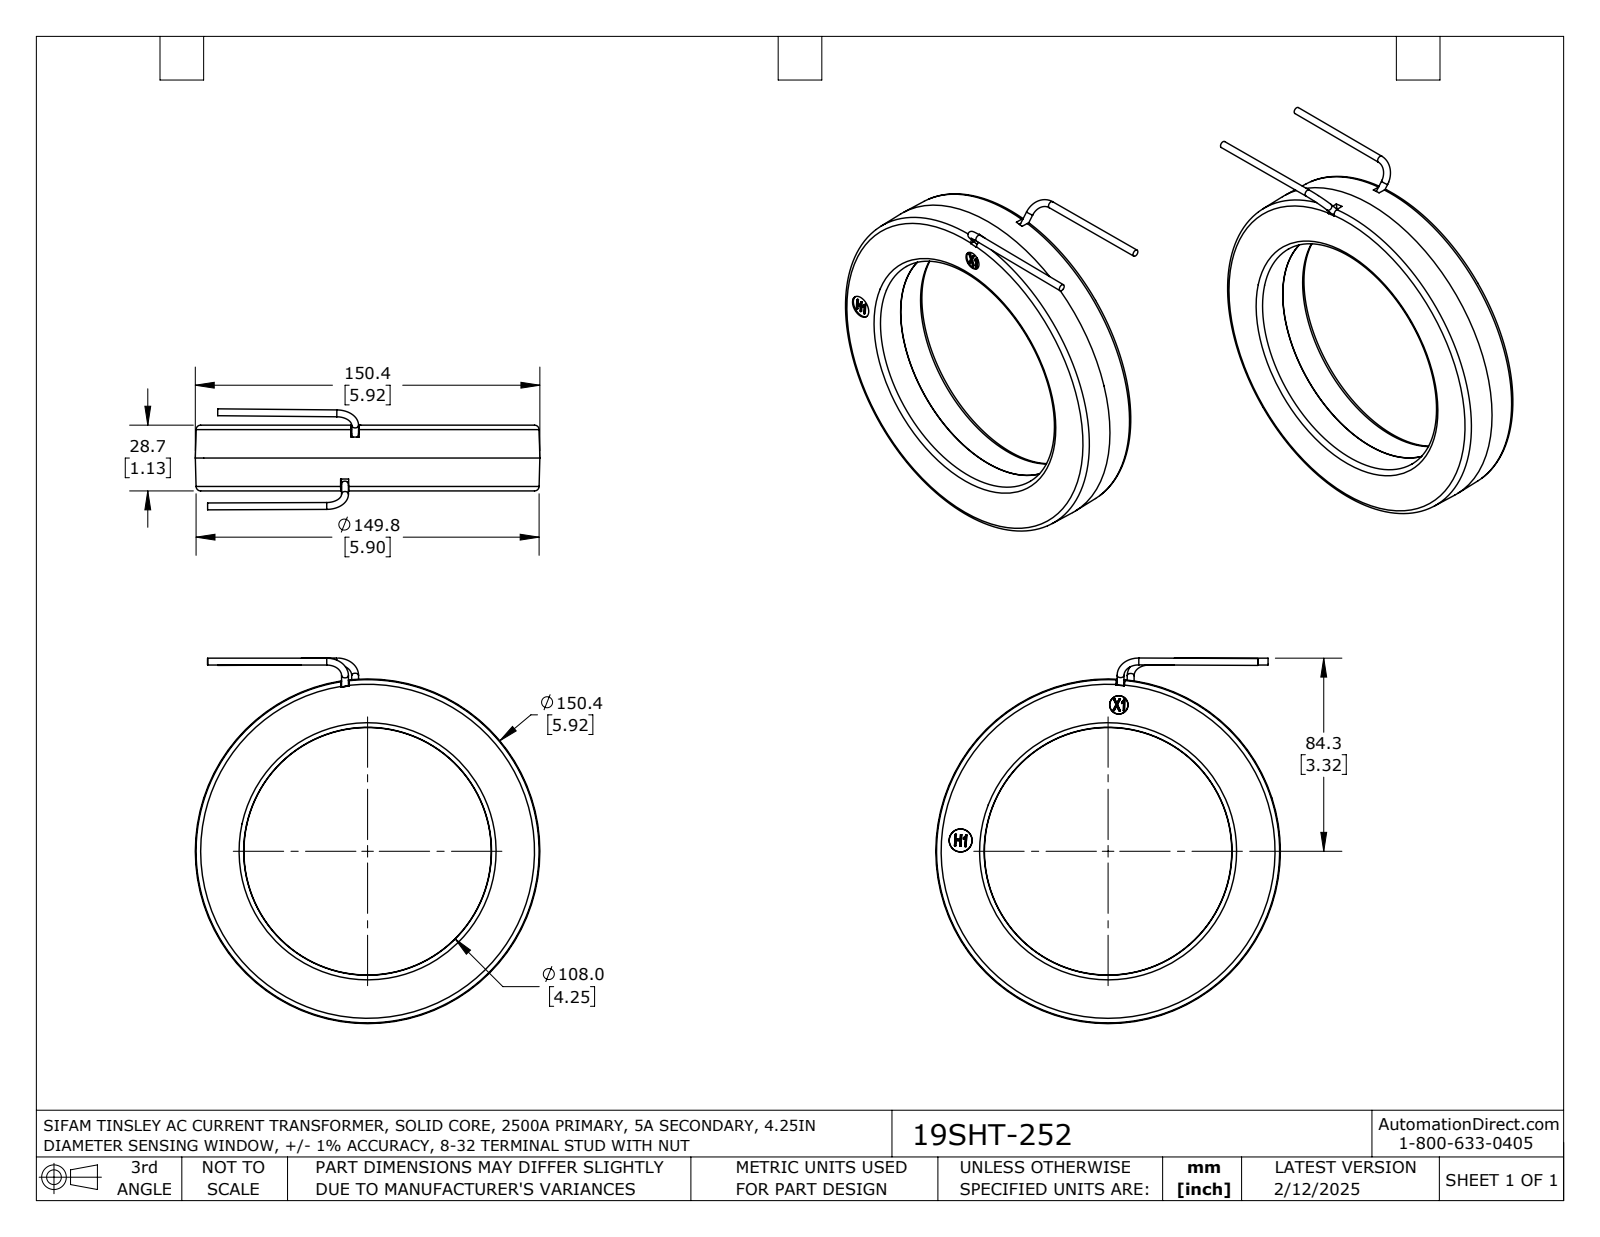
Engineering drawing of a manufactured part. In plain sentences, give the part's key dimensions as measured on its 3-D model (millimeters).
The part is named "19SHT-252". Its 3-D file was written by "SolidWorks 2021 (AUTOMOTIVE_DESIGN)". It is 1 solid with 412 faces: 248 planar, 78 cylindrical and 86 other. Overall it measures 167.9 by 152.4 by 73.9 millimeters. Its volume is 423 900 cubic millimeters and its surface area 105 000 square millimeters. Round bosses or shafts: 2 of diameter 10, 2 of diameter 6, 2 of diameter 5.5, 2 of diameter 4. Partial cylindrical surfaces (rounded edges, fillets, slot ends): 12 of radius 2.8, 8 of radius 1, 8 of radius 2.5, 4 of radius 3.5, 2 of radius 0.3, 2 of radius 1.3, 2 of radius 1.4. The main face-to-face distances are 14.7, 14.6, 1, 29.2, 15.5, 15.6, 30.2, 152.4, 31.2, 156.7.
